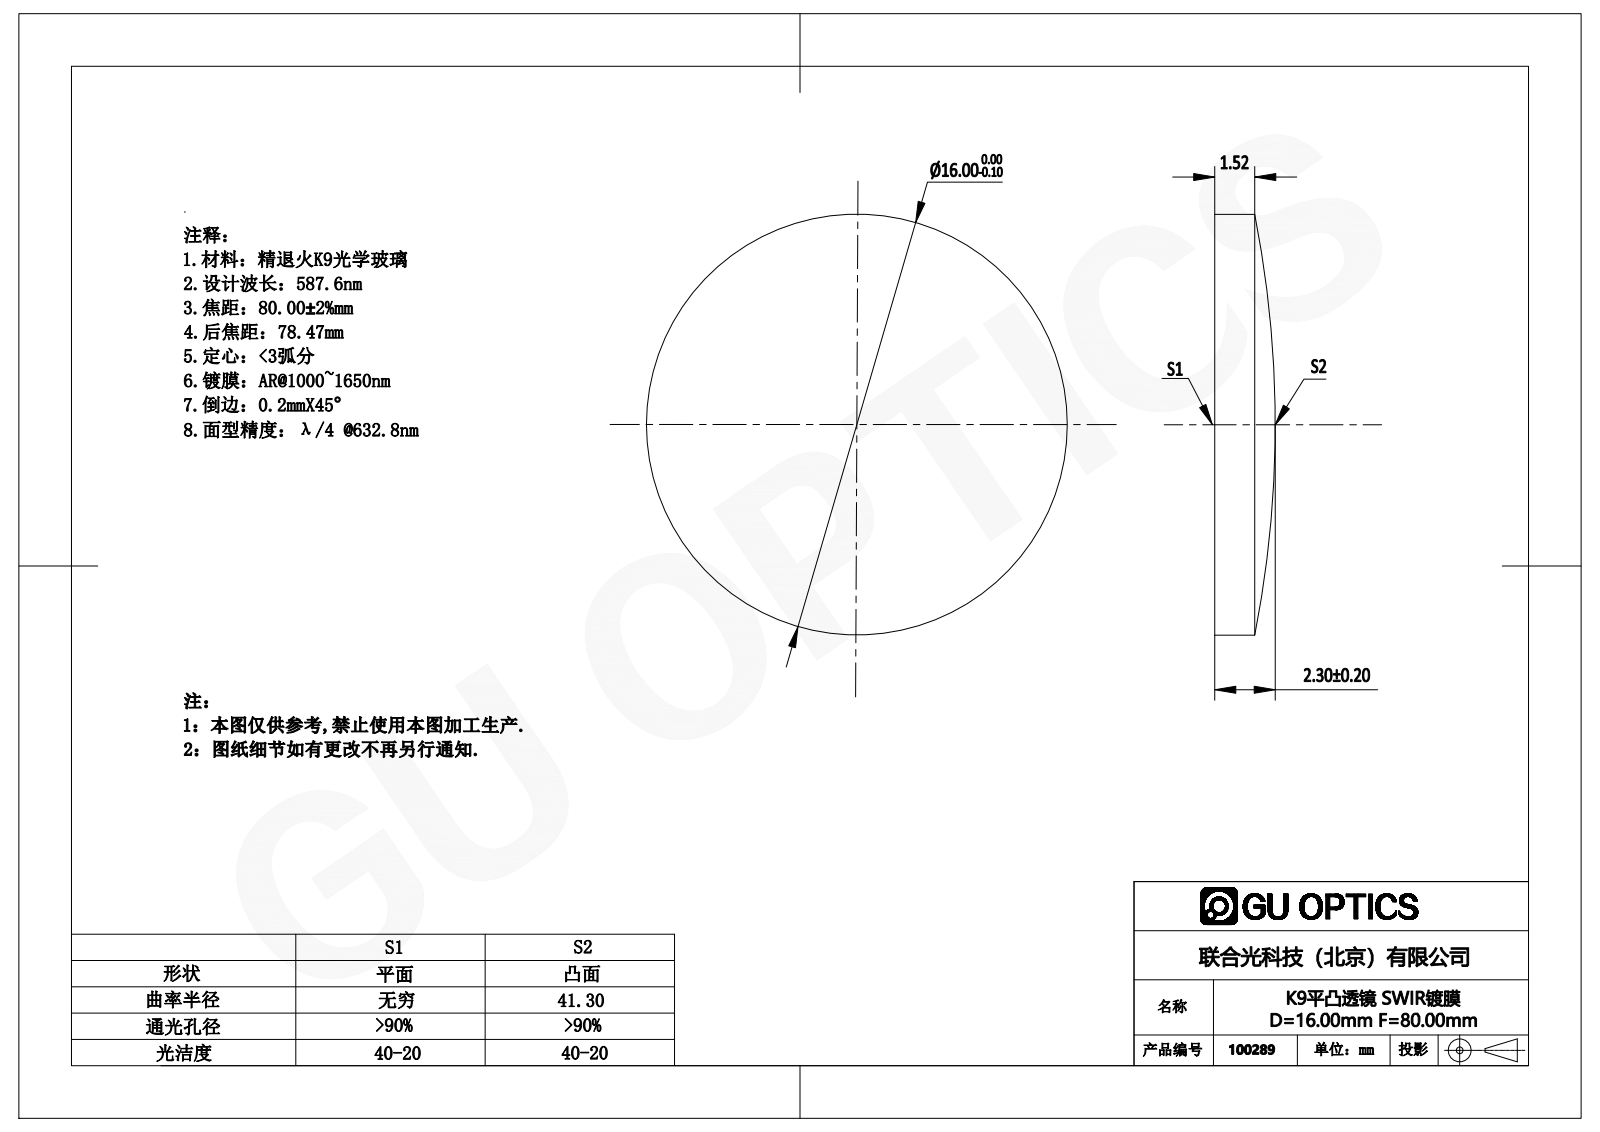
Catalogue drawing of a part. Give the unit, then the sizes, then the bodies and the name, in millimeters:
Units: millimetres
Overall size (bounding box): 16 × 16 × 2.3
Round bosses / shafts (diameter × count): ⌀16 ×1
Volume: 384 mm³ · Surface area: 480 mm²
Bodies: 1 solid, 5 faces (1 planar, 2 cylindrical, 2 other)
Part name (STEP PRODUCT): 100117
STEP written by: SolidWorks 2016 (AUTOMOTIVE_DESIGN)
